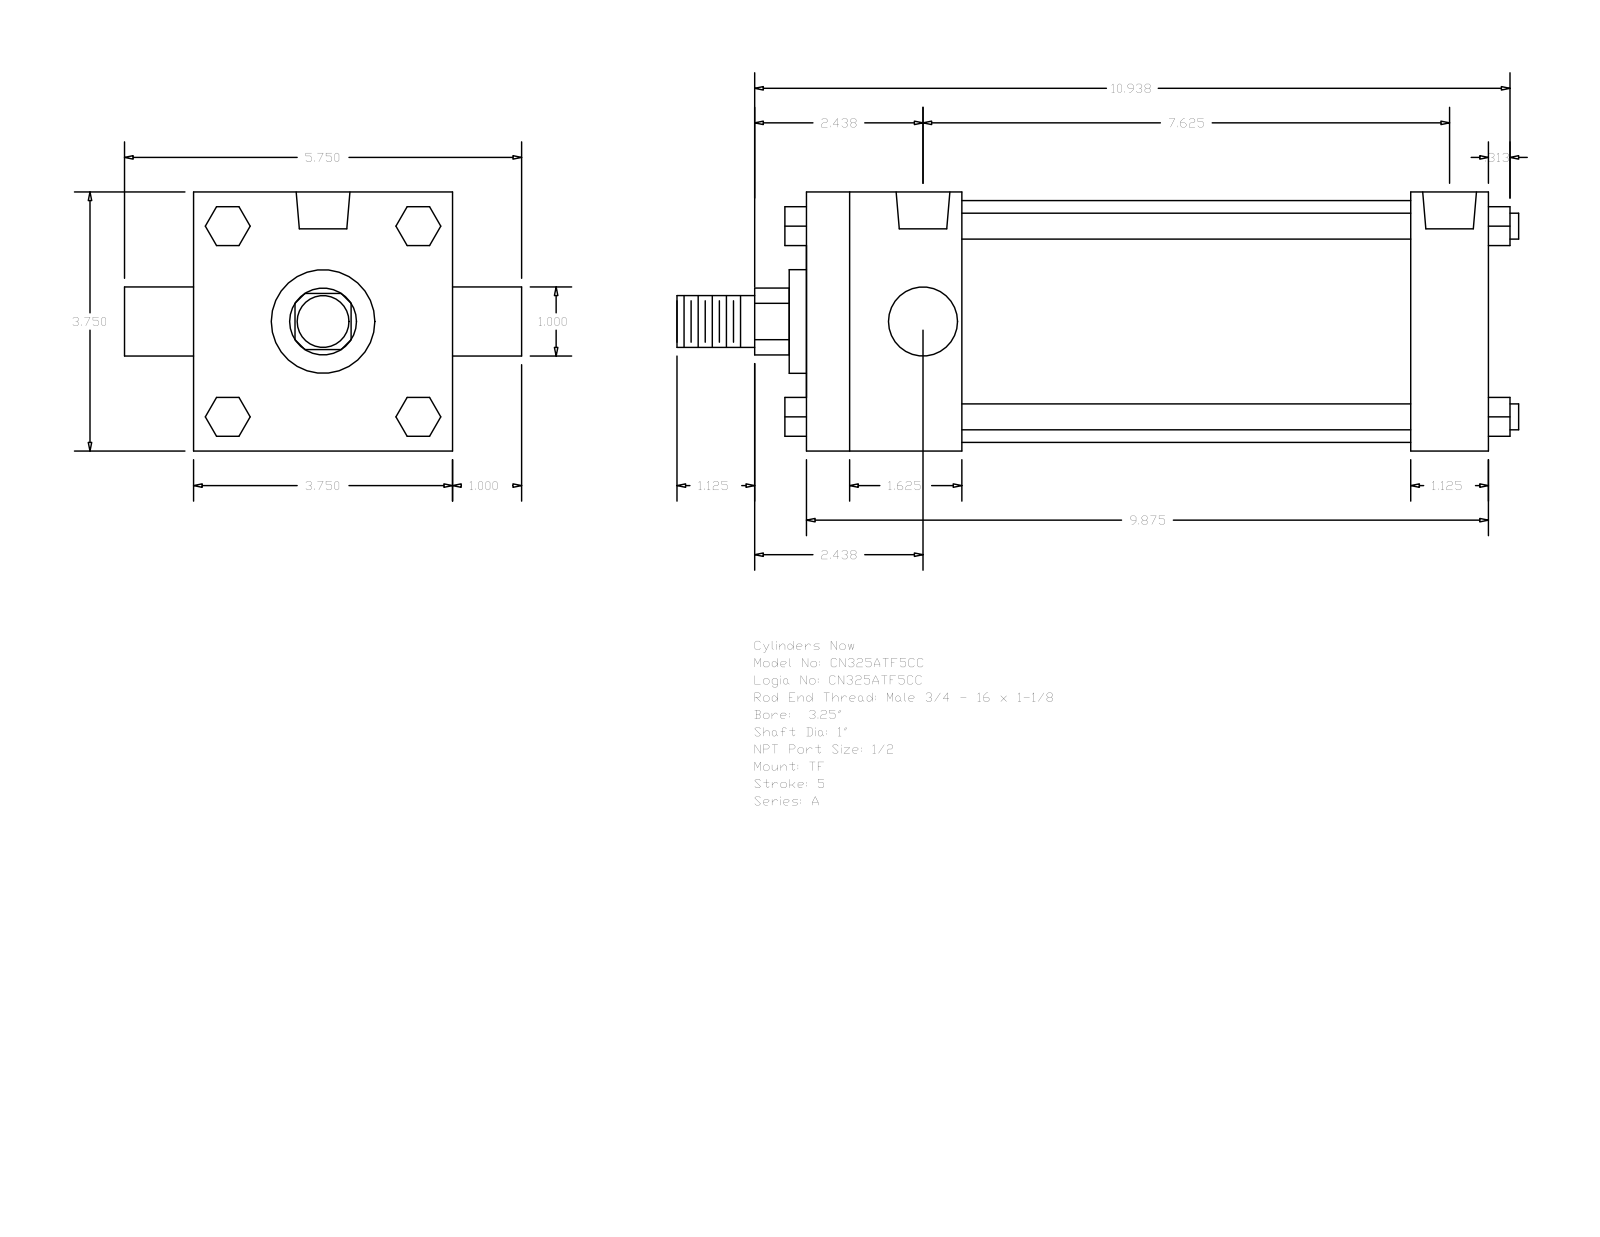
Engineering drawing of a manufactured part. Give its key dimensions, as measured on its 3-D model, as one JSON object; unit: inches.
{"part_name": "A_TF__0325_1", "step_written_by": "GSSL Pune (CONFIG_CONTROL_DESIGN)", "units": "inches", "bodies": {"solids": 0, "faces": 120, "planar": 92, "cylindrical": 28, "other": 0}, "overall_size": [12.187, 5.75, 3.75], "round_holes": [[0.344, 3], [0.778, 2]], "round_bosses_or_shafts": [[0.375, 4], [1, 2], [3.5, 1], [1.5, 1], [0.75, 1]], "partial_cylinders_radius": [[0.484, 1]], "face_to_face_distances": [3.75, 9.875, 2.25, 8.75, 6.5, 7.625, 1.125, 0.562, 1.38, 2.39], "hole_center_spacings": [0.125, 7.5, 7.375, 7.625]}
